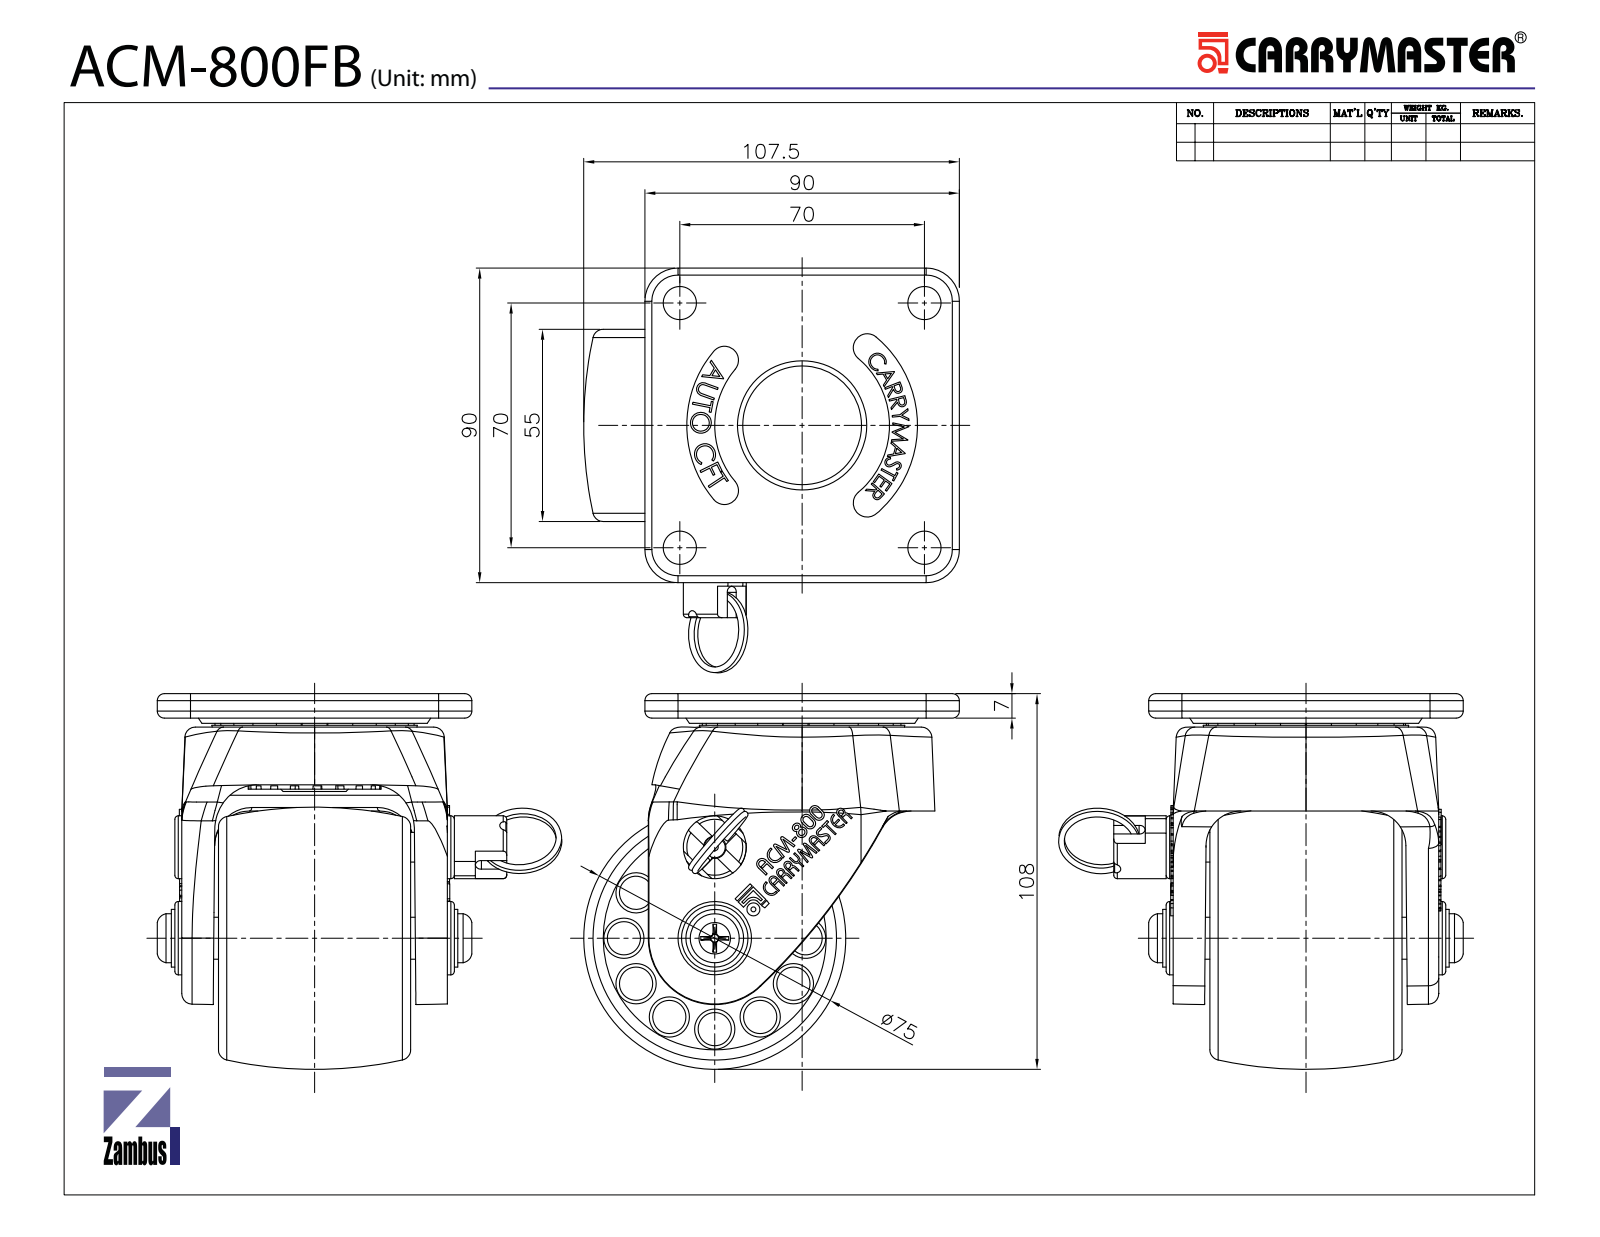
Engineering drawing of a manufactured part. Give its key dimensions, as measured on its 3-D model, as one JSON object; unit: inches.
{"part_name": "ALC-1000F RING-A; ALC-1000F STEEL BALL-白7.15; ACM-800FB-R1; ALC-1000F PIN BOLT (+7 more)", "step_written_by": "SolidWorks 2016 (CONFIG_CONTROL_DESIGN)", "units": "inches", "bodies": {"solids": 48, "faces": 1403, "planar": 623, "cylindrical": 201, "other": 579}, "overall_size": [4.559, 4.232, 4.231], "volume_in3": 25.43, "surface_area_in2": 158, "round_holes": [[0.374, 16], [0.056, 1], [0.118, 1], [0.252, 1], [0.268, 1], [0.343, 1], [0.362, 1], [0.394, 1], [0.512, 1], [0.709, 1], [0.787, 1], [1.575, 1]], "round_bosses_or_shafts": [[1.622, 1], [1.496, 1], [0.984, 1], [0.945, 1], [0.827, 1], [0.709, 1], [0.65, 1], [0.551, 1]], "partial_cylinders_radius": [[0.079, 8], [0.157, 4], [0.374, 4], [0.049, 2], [0.058, 2], [0.069, 2], [0.394, 2], [0.512, 2]], "face_to_face_distances": [0.276, 2.579, 0.413, 0.689, 0.059, 0.039, 2.303, 1.89, 2.165, 0.079], "hole_center_spacings": [1.024, 0.53, 1.448, 1.978, 1.773, 1.773, 1.949, 2.048]}
